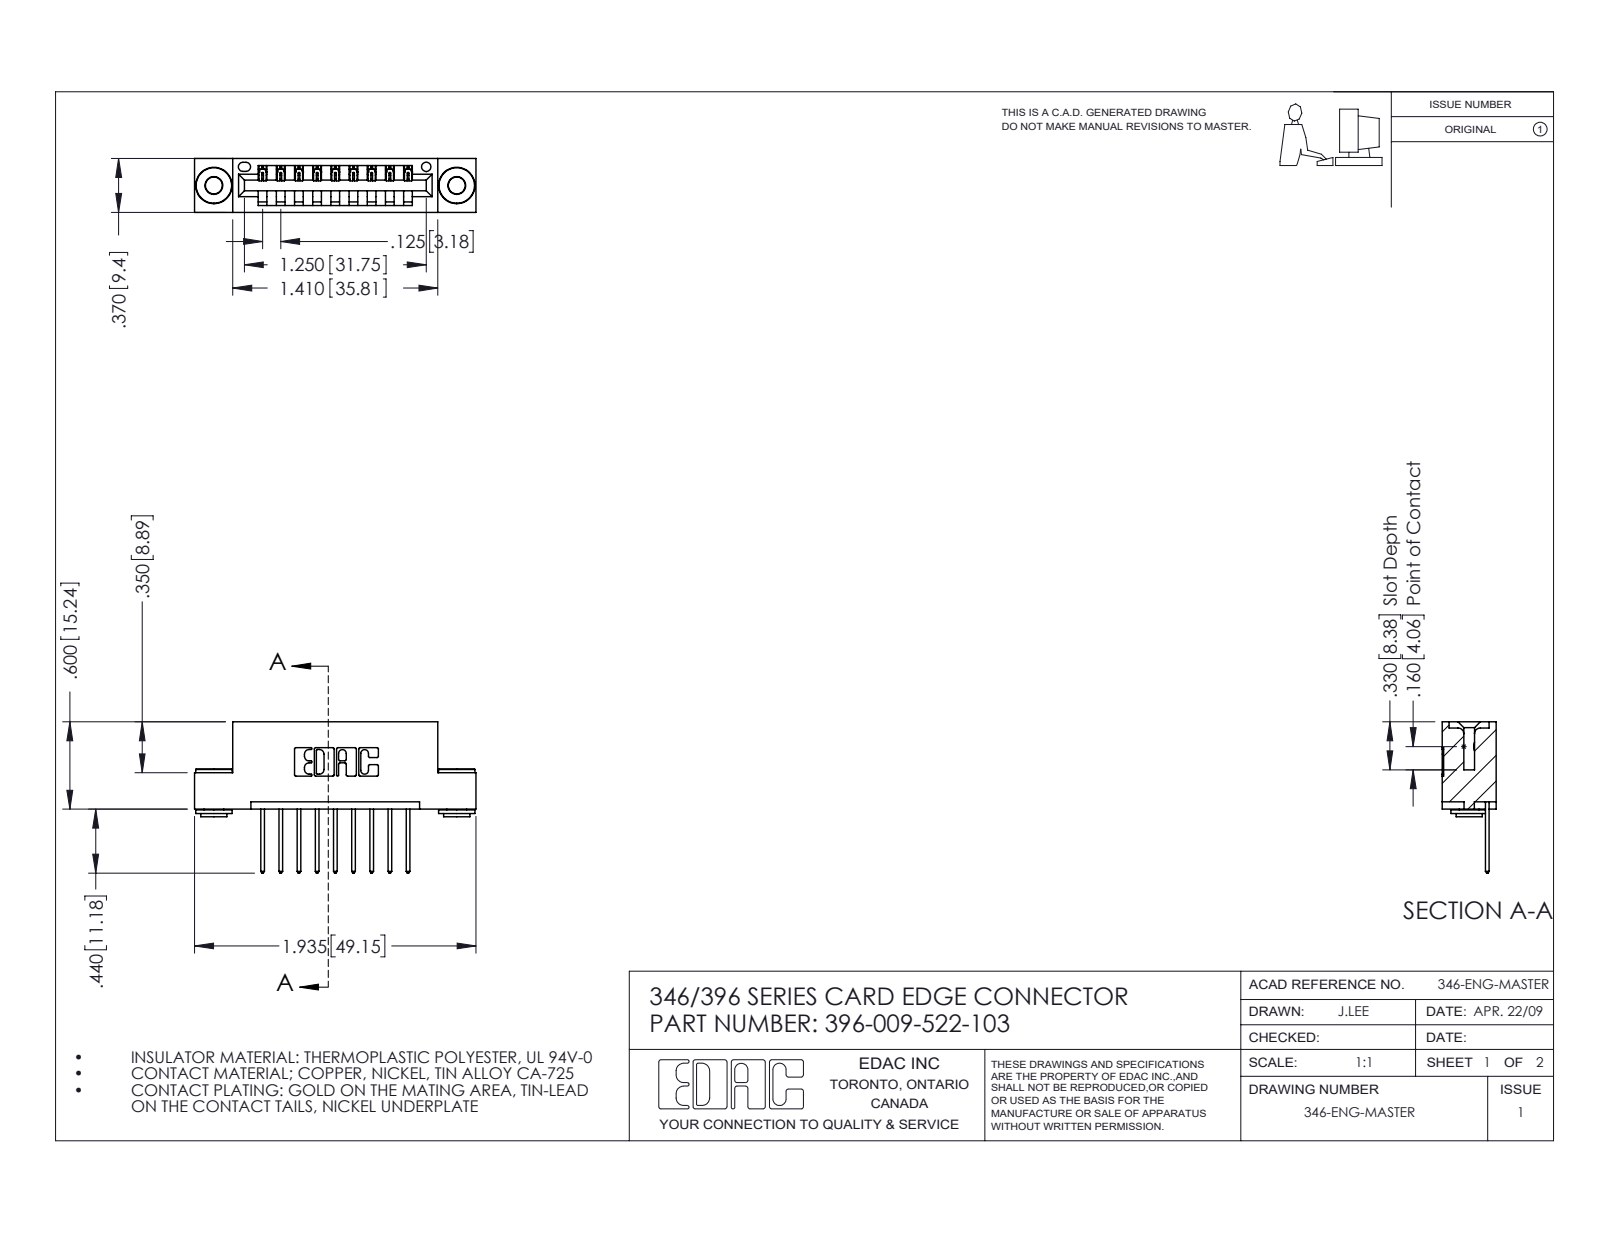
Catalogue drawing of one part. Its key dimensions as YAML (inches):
part_name: "346 Part_Flush Mounting Lugs - 0.156 Dia-TH; 345-250-002_345-250-002-102; 396-009-522-103; 345-292-001_345-293-122"
step_written_by: "SolidWorks 2016 (CONFIG_CONTROL_DESIGN)"
units: inches
bodies: {solids: 12, faces: 682, planar: 446, cylindrical: 228, other: 8}
overall_size: [1.935, 1.04, 0.37]
volume: 0.274
surface_area: 8.553
round_holes:
  - {diameter: 0.116, count: 2}
  - {diameter: 0.156, count: 2}
  - {diameter: 0.064, count: 1}
round_bosses_or_shafts:
  - {diameter: 0.25, count: 2}
  - {diameter: 0.18, count: 2}
  - {diameter: 0.136, count: 2}
partial_cylinders:
  - {radius: 0.01, count: 22}
  - {radius: 0.006, count: 18}
  - {radius: 0.01, count: 18}
  - {radius: 0.007, count: 6}
  - {radius: 0.031, count: 6}
  - {radius: 0.026, count: 3}
  - {radius: 0.031, count: 2}
  - {radius: 0.04, count: 2}
face_to_face_distances: [0.25, 0.048, 0.322, 0.37, 0.025, 0.072, 0.298, 0.148, 0.222, 0.1]
hole_center_spacings: [0.246, 1.465, 1.67]
